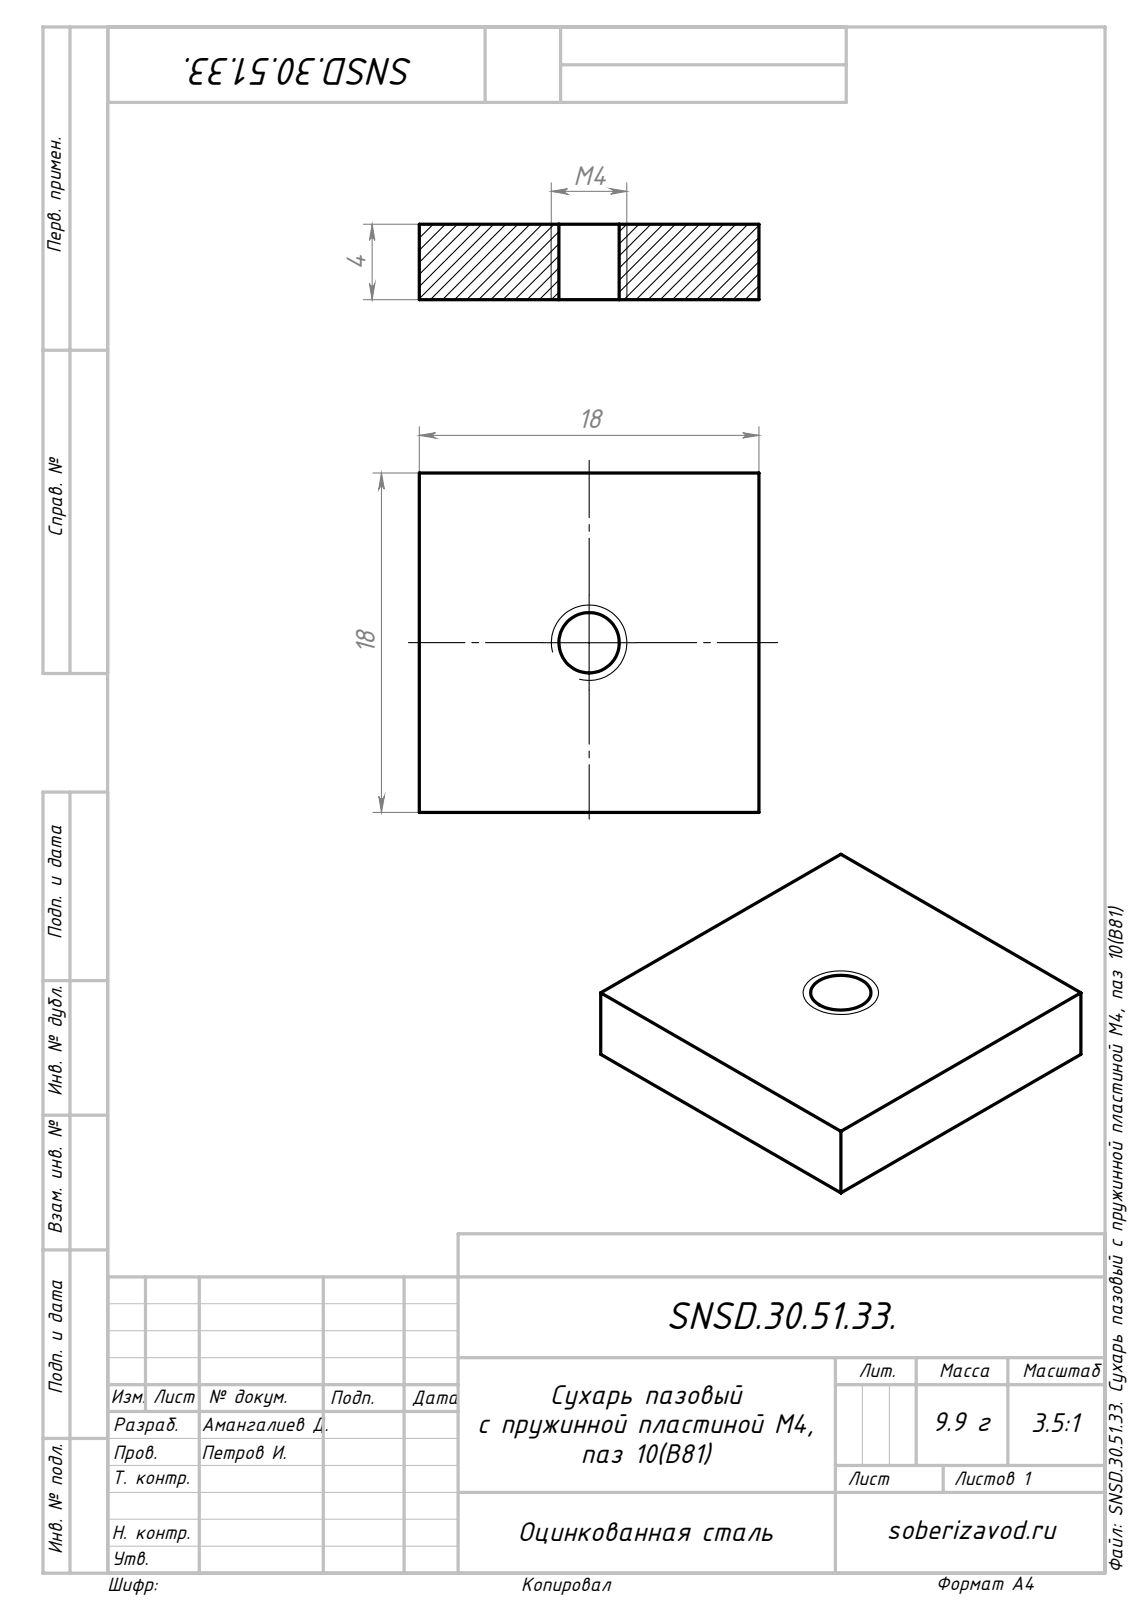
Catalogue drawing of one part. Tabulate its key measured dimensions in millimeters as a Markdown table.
| quantity | value |
| --- | --- |
| part name | SNSD.30.51.33. Сухарь пазовый с пружинной пластиной M4, паз 10(B81); SNSD.30.51.19. Сухарь пазовый с пружинной пластиной M6, паз 8(B79)B80B78B81_00 |
| STEP written by | SolidWorks 2017 (AUTOMOTIVE_DESIGN) |
| units | millimeters |
| bodies | 1 solid, 8 faces (6 planar, 2 cylindrical, 0 other) |
| overall size | 18 × 18 × 4 |
| volume | 1 264 mm³ |
| surface area | 960 mm² |
| round holes (diameter × count) | 3.2 × 1 |
| main face-to-face distances | 4, 18 |
